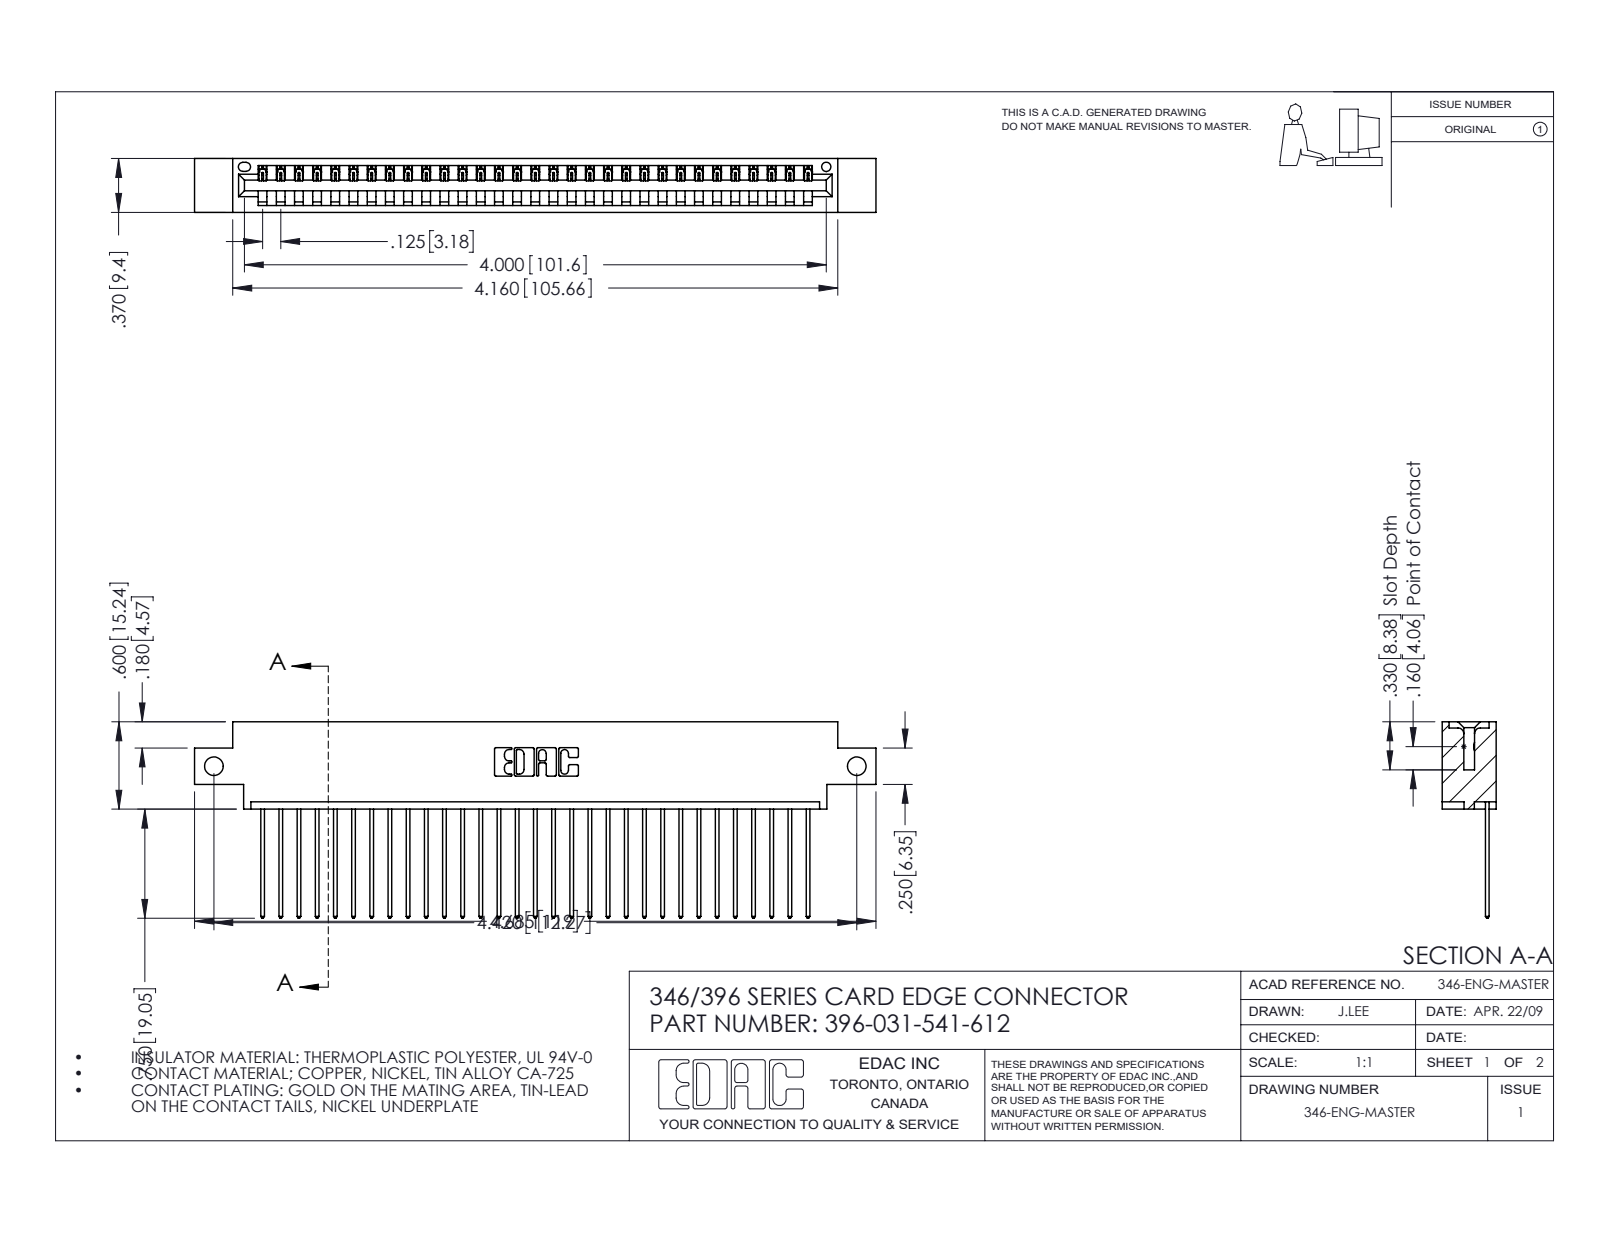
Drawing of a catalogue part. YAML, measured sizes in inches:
part_name: "346 Part_0.170 Offset - Side Mount; 396-031-541-612; 345-292-001_345-293-141"
step_written_by: "SolidWorks 2016 (CONFIG_CONTROL_DESIGN)"
units: inches
bodies: {solids: 32, faces: 1924, planar: 1320, cylindrical: 604, other: 0}
overall_size: [4.685, 1.35, 0.37]
volume: 0.682
surface_area: 22.44
round_holes:
  - {diameter: 0.128, count: 2}
  - {diameter: 0.064, count: 1}
partial_cylinders:
  - {radius: 0.006, count: 62}
  - {radius: 0.01, count: 62}
  - {radius: 0.01, count: 22}
  - {radius: 0.007, count: 6}
  - {radius: 0.031, count: 6}
  - {radius: 0.026, count: 3}
  - {radius: 0.031, count: 2}
  - {radius: 0.04, count: 2}
face_to_face_distances: [0.048, 0.322, 0.37, 0.25, 0.072, 0.298, 0.025, 0.148, 0.222, 0.1]
hole_center_spacings: [4.42]
